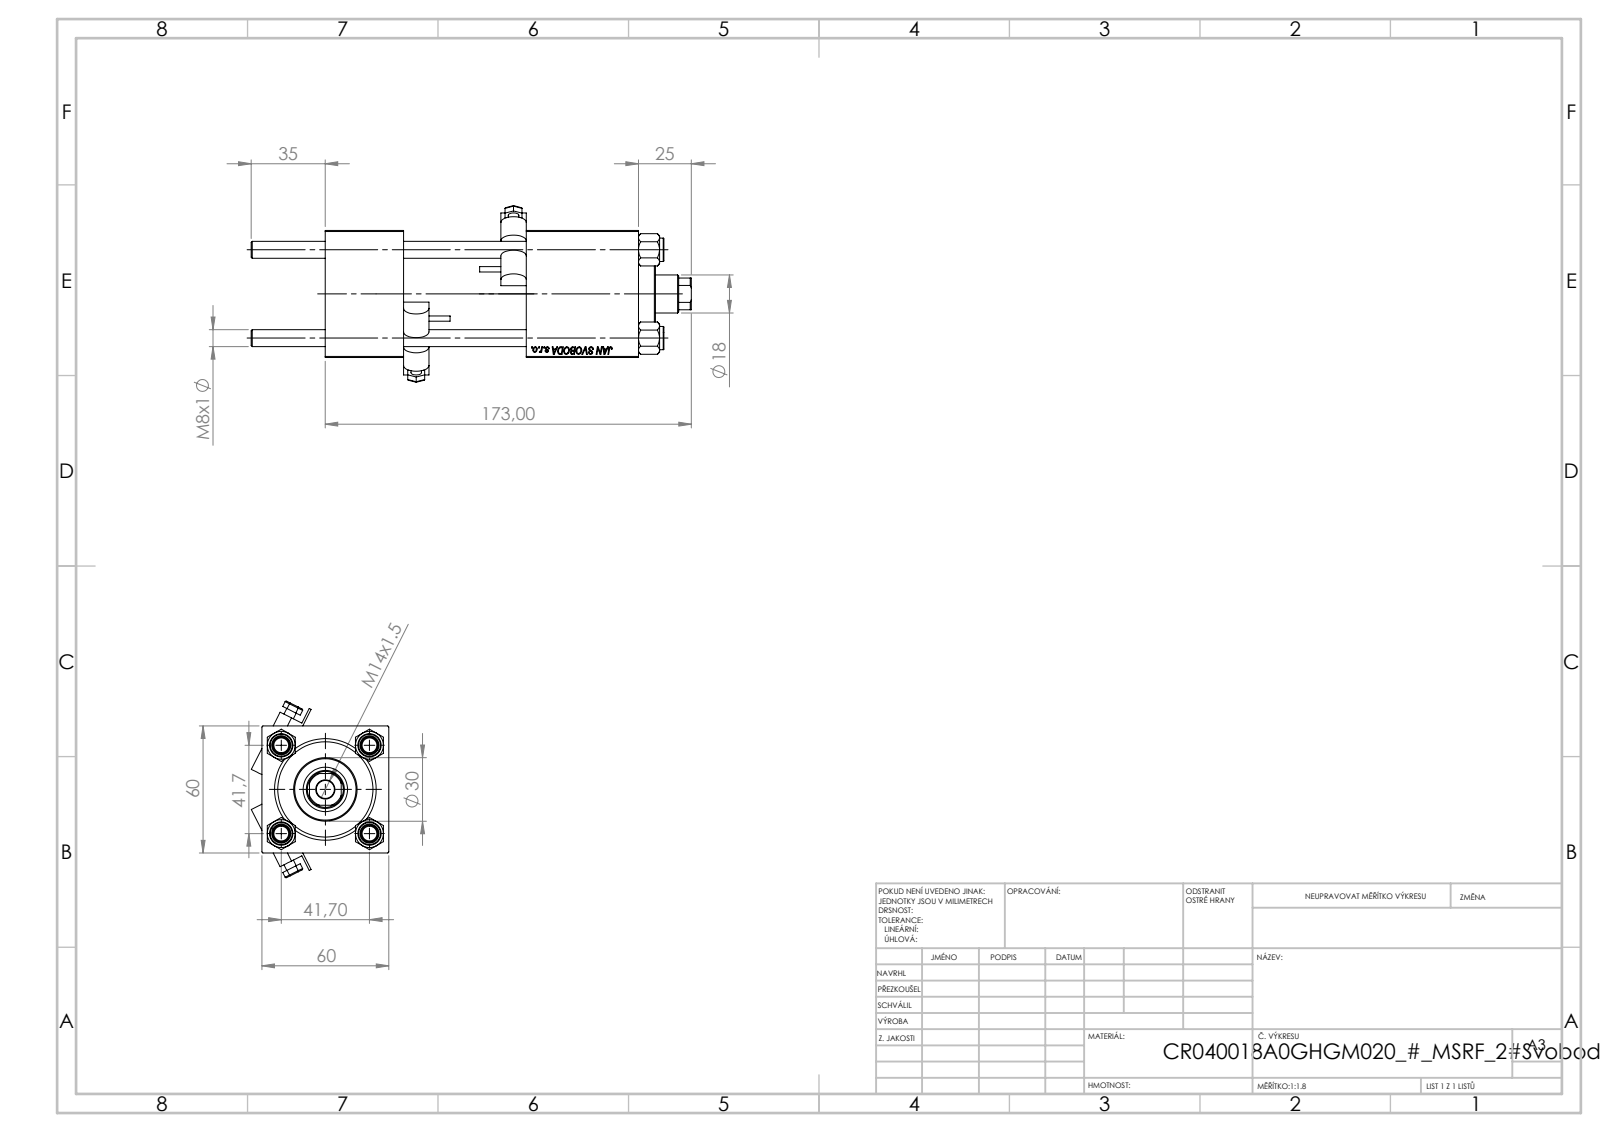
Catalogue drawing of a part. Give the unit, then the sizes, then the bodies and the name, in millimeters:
Units: millimetres
Overall size (bounding box): 208 × 83.44 × 64.97
Round holes (diameter × count): ⌀8 ×4, ⌀7 ×2, ⌀16.66 ×2, ⌀24 ×2, ⌀8.5 ×1, ⌀18 ×1, ⌀21 ×1, ⌀31 ×1, ⌀40 ×1, ⌀45 ×1
Round bosses / shafts (diameter × count): ⌀11 ×4, ⌀5 ×2, ⌀2.5 ×2, ⌀46 ×1, ⌀30 ×1
Partial cylindrical surfaces — rounded edges, fillets, slot ends (radius × count): R0.5 ×12, R6 ×4, R8.5 ×1
Main face-to-face distances: 60, 37, 111, 148, 58, 53, 95, 119.3, 82.3, 24.3
Hole centre spacings: 29.49, 41.7, 58.97, 92.5
Volume: 420 973 mm³ · Surface area: 118 299 mm²
Bodies: 13 solids, 1199 faces (557 planar, 106 cylindrical, 536 other)
Part name (STEP PRODUCT): V215CR_BODY_A; V215CR_VCP; CR025_012_A_0_G_A_G_M_020_+#_##_TYCINKA; NUT_M5 (+2 more)
STEP written by: SolidWorks 2019 (CONFIG_CONTROL_DESIGN)
